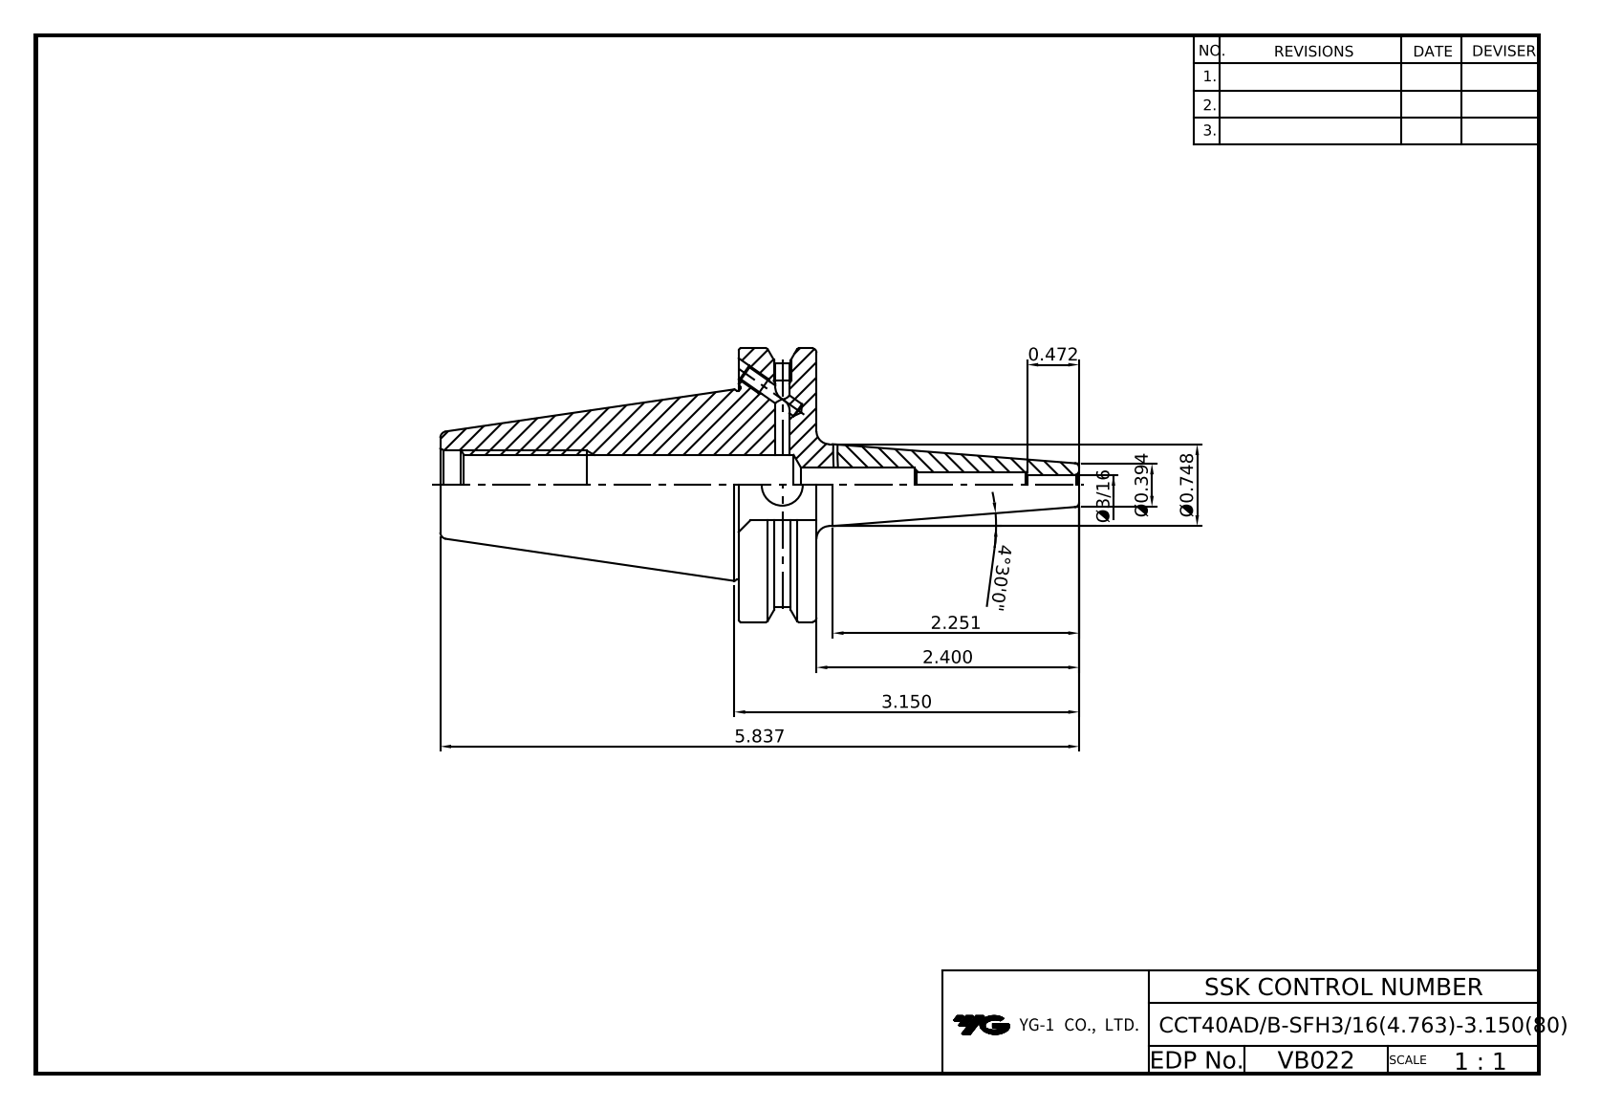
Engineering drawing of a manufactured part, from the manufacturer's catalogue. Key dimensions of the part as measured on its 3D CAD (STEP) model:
Part name (STEP PRODUCT): LO-CCT40ADB-SFH4.7625-80
STEP written by: Autodesk Inventor 2022 (AUTOMOTIVE_DESIGN)
Units: millimetres
Bodies: 1 solid, 89 faces (36 planar, 29 cylindrical, 24 other)
Overall size (bounding box): 148.25 × 63.5 × 61.09
Volume: 112 395 mm³ · Surface area: 25 079 mm²
Round holes (diameter × count): ⌀3.24 ×4, ⌀4 ×2, ⌀4.2 ×2, ⌀4.76 ×1, ⌀6 ×1, ⌀8 ×1, ⌀9.53 ×1, ⌀13 ×1, ⌀13.39 ×1, ⌀16.3 ×1
Round bosses / shafts (diameter × count): ⌀63.5 ×1, ⌀43.8 ×1, ⌀19 ×1
Partial cylindrical surfaces — rounded edges, fillets, slot ends (radius × count): R28.15 ×1
Main face-to-face distances: 18.05, 47.6, 16.38, 69.25, 87.3, 81.34, 12.09, 5.96, 77.51, 8.26
